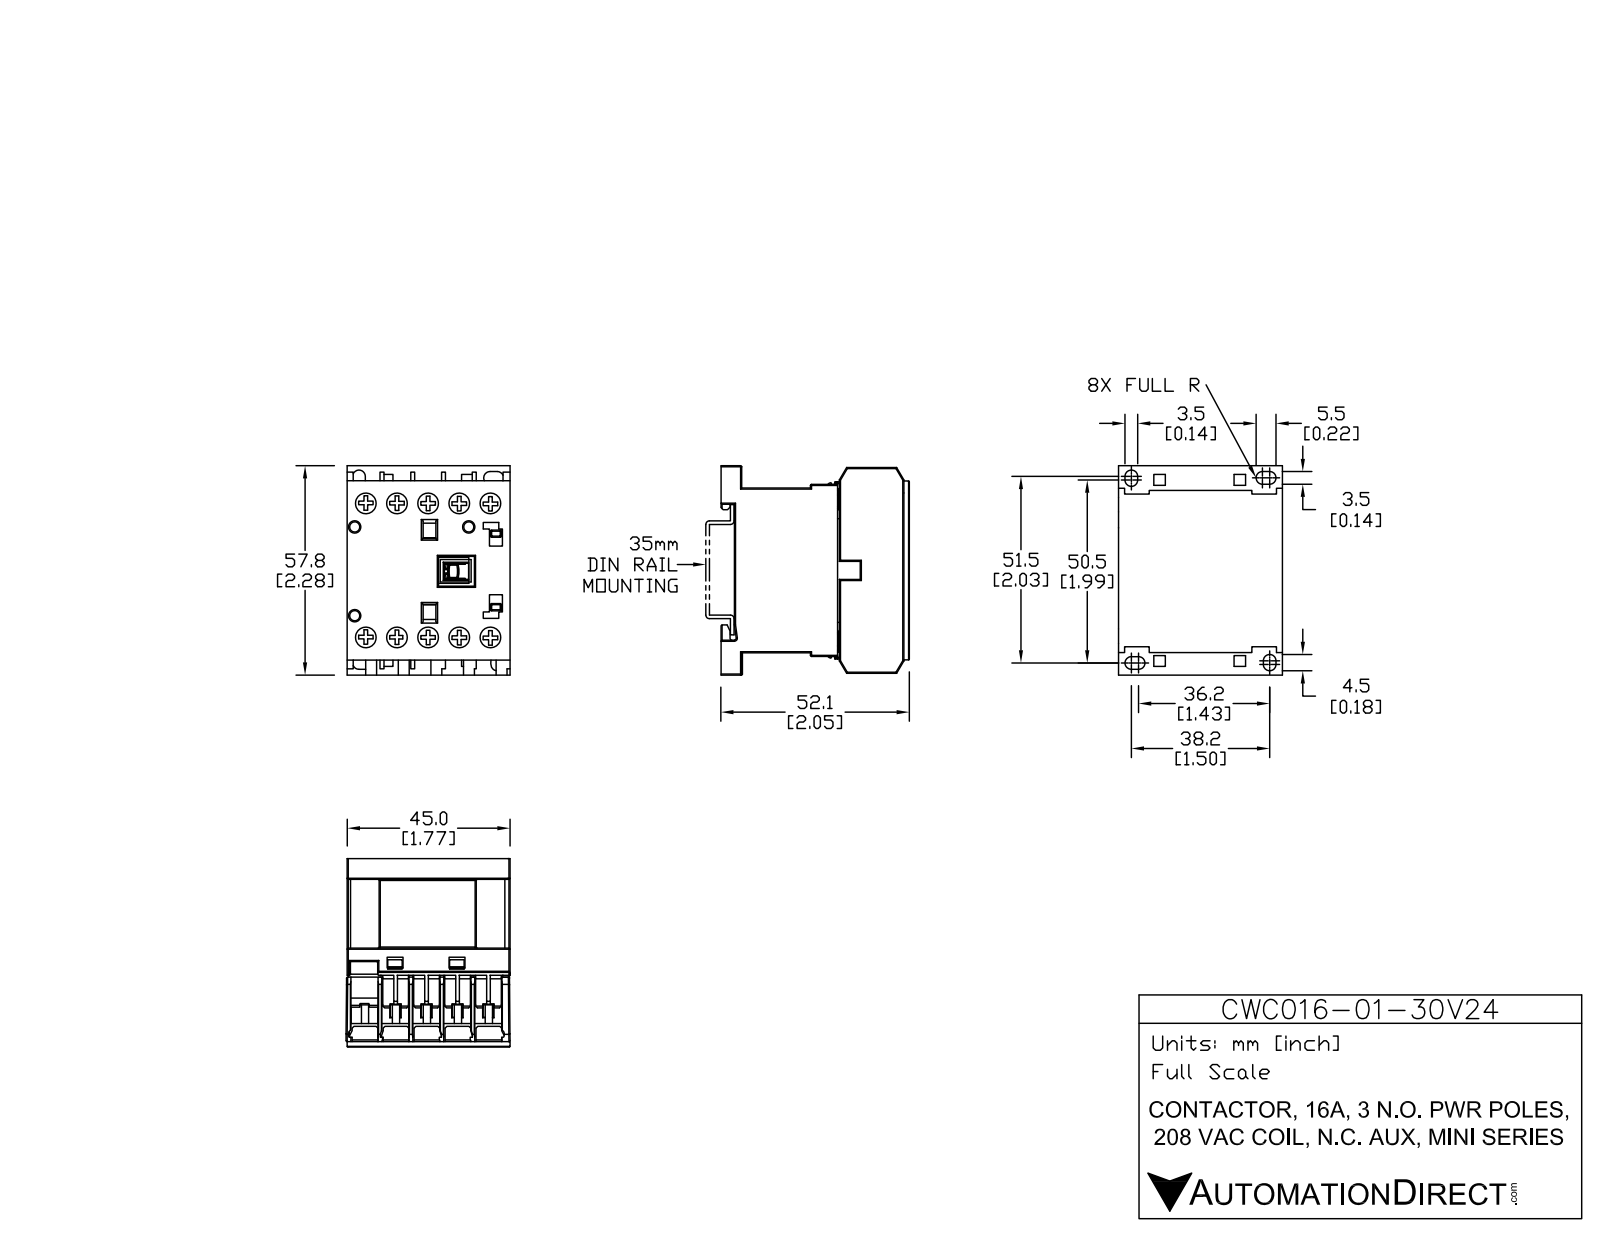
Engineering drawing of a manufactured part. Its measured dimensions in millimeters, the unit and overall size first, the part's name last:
Units: millimetres
Overall size (bounding box): 58.04 × 52.12 × 45.75
Round holes (diameter × count): ⌀6.2 ×10, ⌀2.8 ×3
Round bosses / shafts (diameter × count): ⌀5.9 ×10
Partial cylindrical surfaces — rounded edges, fillets, slot ends (radius × count): R0.3 ×20, R1.72 ×6, R1.73 ×2, R0.32 ×1, R0.42 ×1, R0.55 ×1
Main face-to-face distances: 8.25, 45.5, 1.25, 16.5, 9.5, 5.5, 17.75, 5.13, 10.63, 7
Hole centre spacings: 8.55, 37.94, 17.1, 40.72, 36.96, 25.65, 44.99, 6.91
Volume: 97 133 mm³ · Surface area: 30 437 mm²
Bodies: 15 solids, 535 faces (445 planar, 90 cylindrical, 0 other)
Part name (STEP PRODUCT): CWC16-01-30V24
STEP written by: SolidWorks 2013 (AUTOMOTIVE_DESIGN)
